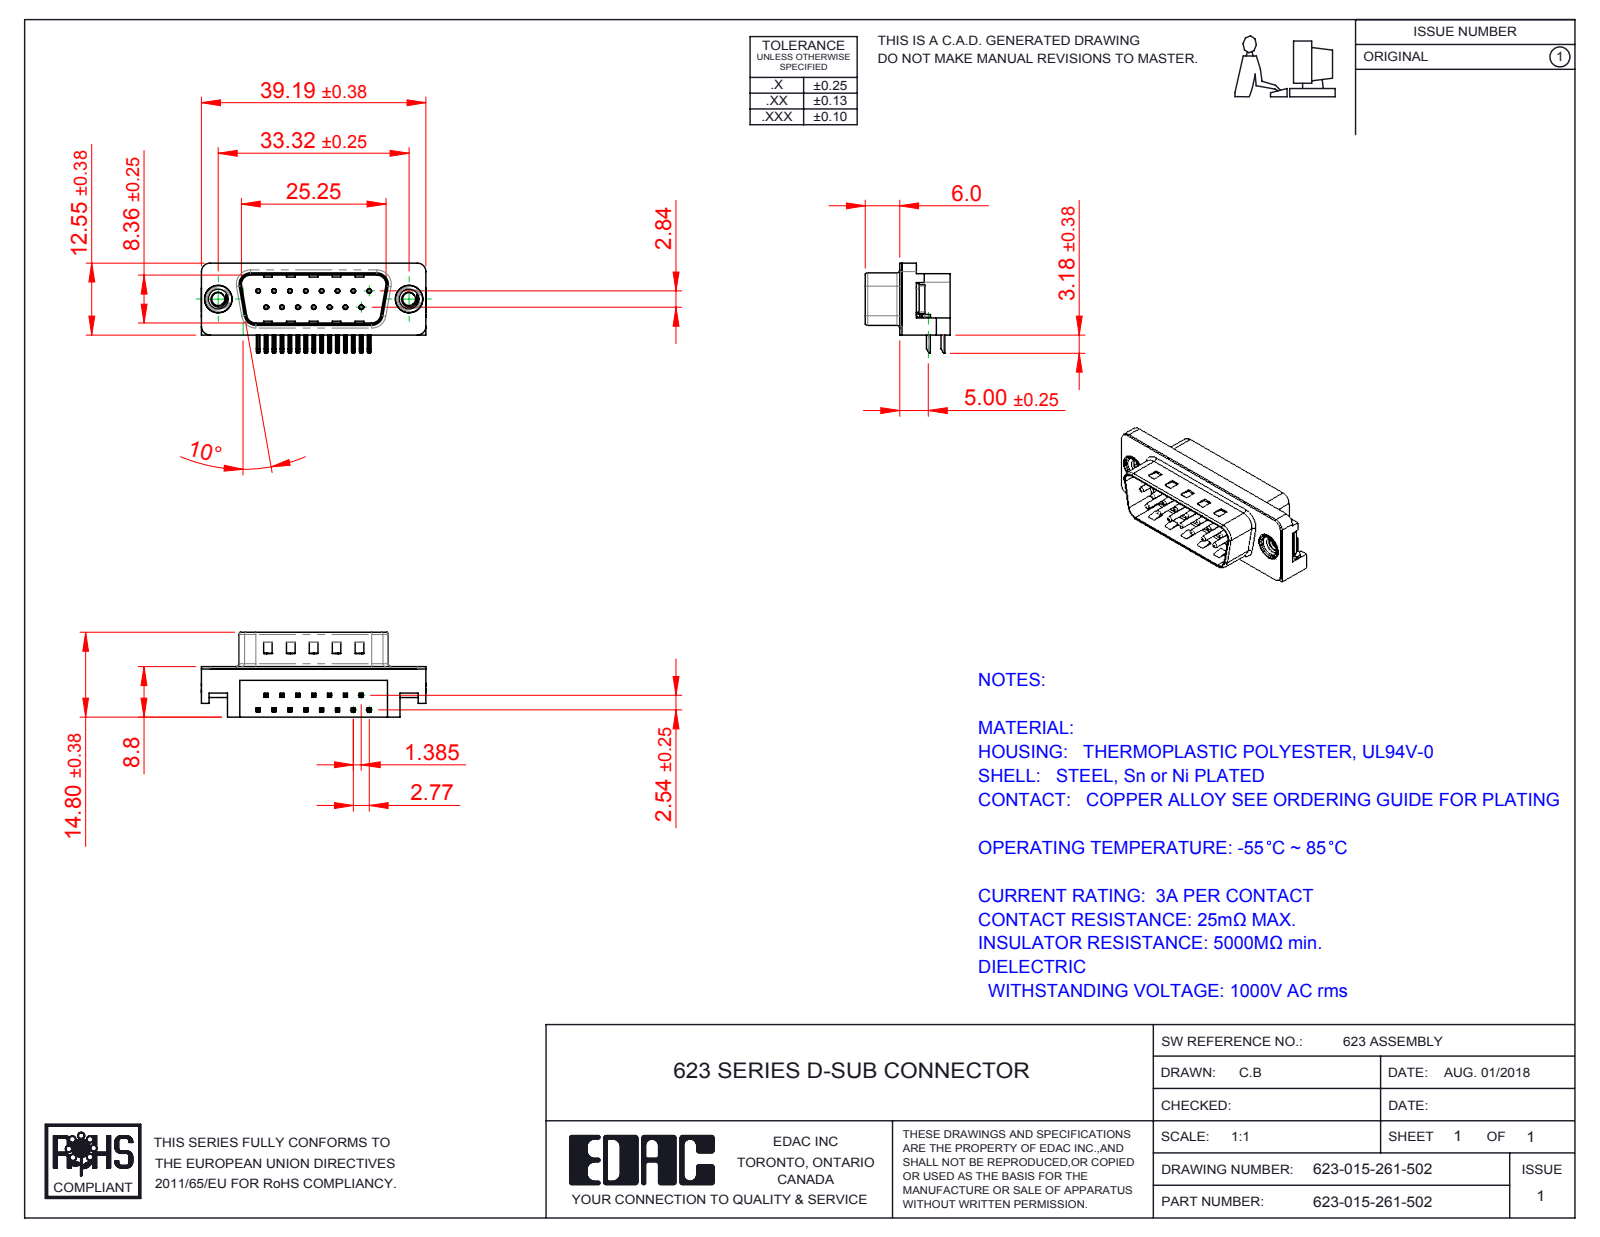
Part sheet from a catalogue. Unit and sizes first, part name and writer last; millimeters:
Units: millimetres
Overall size (bounding box): 39.22 × 15.73 × 14.8
Round holes (diameter × count): ⌀0.35 ×15, ⌀0.8 ×15, ⌀2.26 ×2, ⌀4 ×2, ⌀4.8 ×2, ⌀5 ×2
Round bosses / shafts (diameter × count): ⌀0.75 ×15, ⌀4.9 ×2, ⌀4.75 ×2, ⌀3.9 ×2
Partial cylindrical surfaces — rounded edges, fillets, slot ends (radius × count): R0.25 ×68, R0.12 ×30, R1 ×16, R0.5 ×9, R1.5 ×6, R0.9 ×4, R1.6 ×4, R2 ×4
Main face-to-face distances: 0.4, 8.4, 2.1, 1.7, 10.46, 8.8, 10.86, 8.76, 5.9, 2.9
Hole centre spacings: 3.16, 2.77, 5.54, 8.31, 11.08, 5.03, 5.04, 7.48
Volume: 3 319 mm³ · Surface area: 4 885 mm²
Bodies: 21 solids, 1467 faces (893 planar, 435 cylindrical, 139 other)
Part name (STEP PRODUCT): 623 Non Board Mount; 623 4-40 Threaded Rivet; 623 Shell_15 Socket; 623 Contact Top (+3 more)
STEP written by: SolidWorks 2016 (CONFIG_CONTROL_DESIGN)
